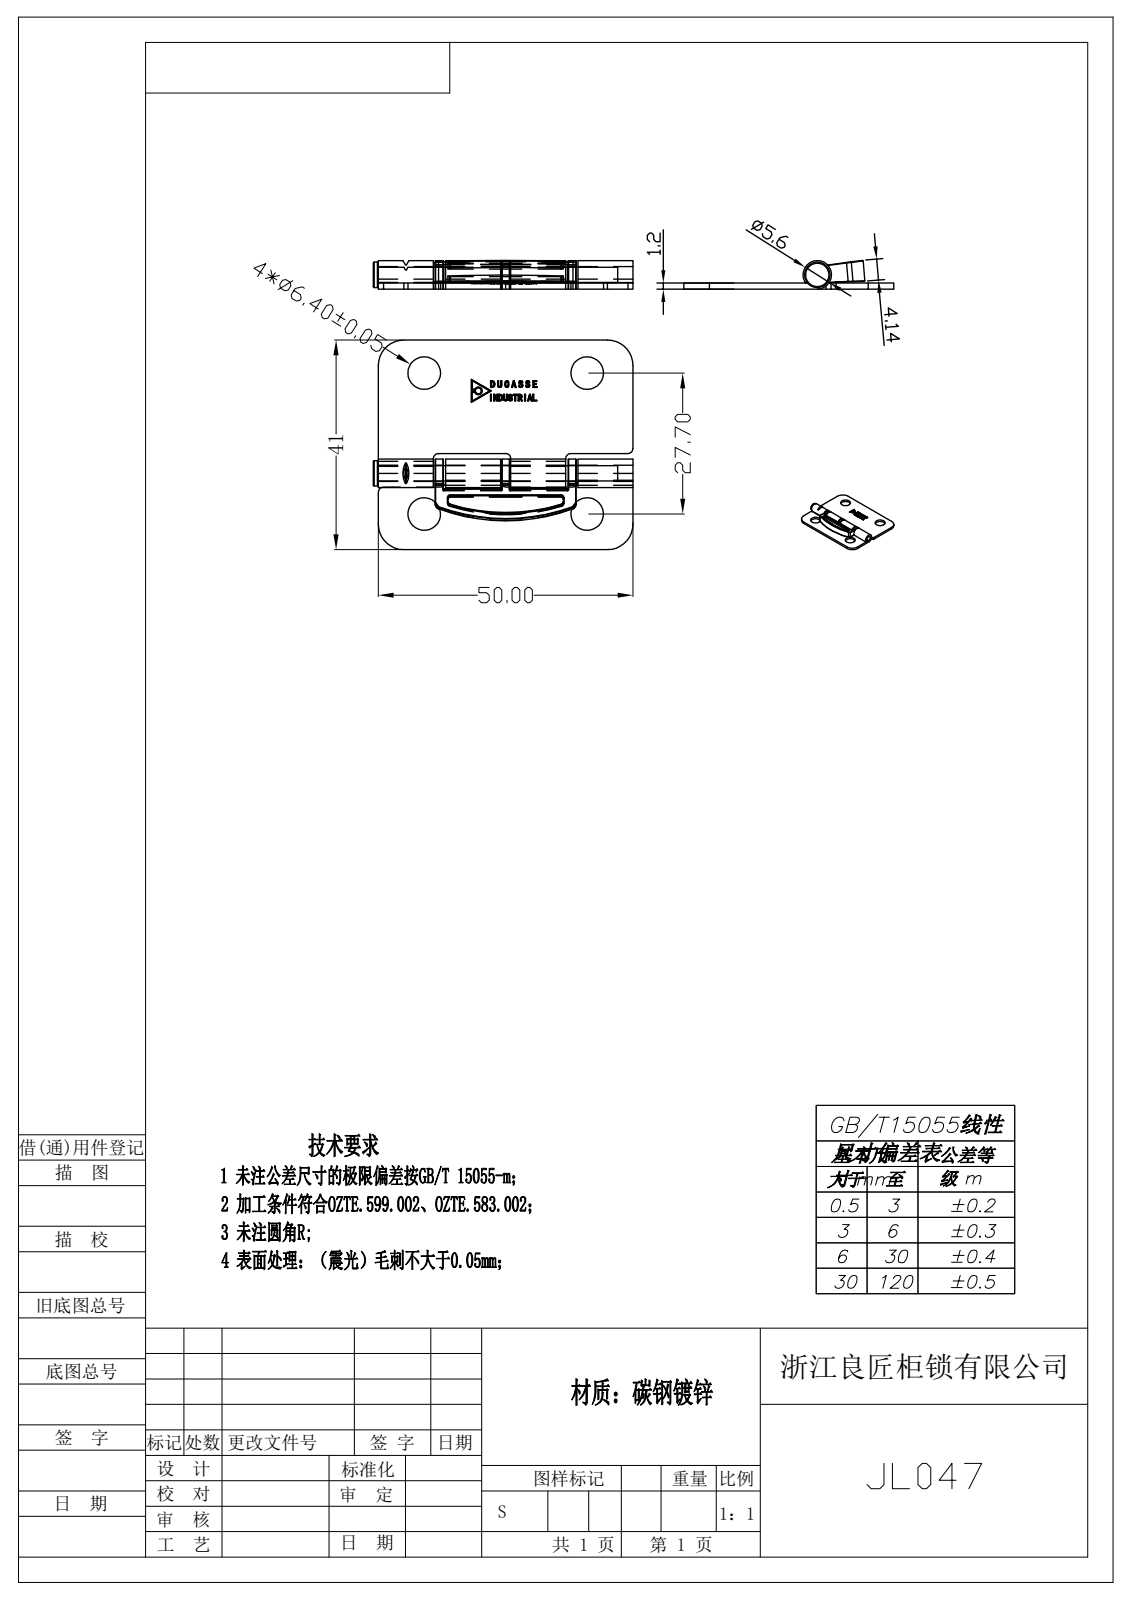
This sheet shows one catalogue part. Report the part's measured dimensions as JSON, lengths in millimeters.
{"step_written_by": "Rhino 8.5 (CONFIG_CONTROL_DESIGN)", "units": "millimeters", "bodies": {"solids": 4, "faces": 483, "planar": 202, "cylindrical": 97, "other": 184}, "overall_size": [51, 41.2, 5.66], "volume_mm3": 3504, "surface_area_mm2": 6354, "round_holes": [[6.4, 4], [3.2, 1]], "round_bosses_or_shafts": [[5.6, 1], [5, 1], [3, 1]], "partial_cylinders_radius": [[0.1, 27], [1, 10], [0.5, 4], [5, 4], [36.89, 1], [38.19, 1]], "face_to_face_distances": [1.2, 13.05, 26, 10.8, 13.2, 1.5, 11.15, 38.85, 1.6, 41.2], "hole_center_spacings": [27.7, 32, 42.32]}
